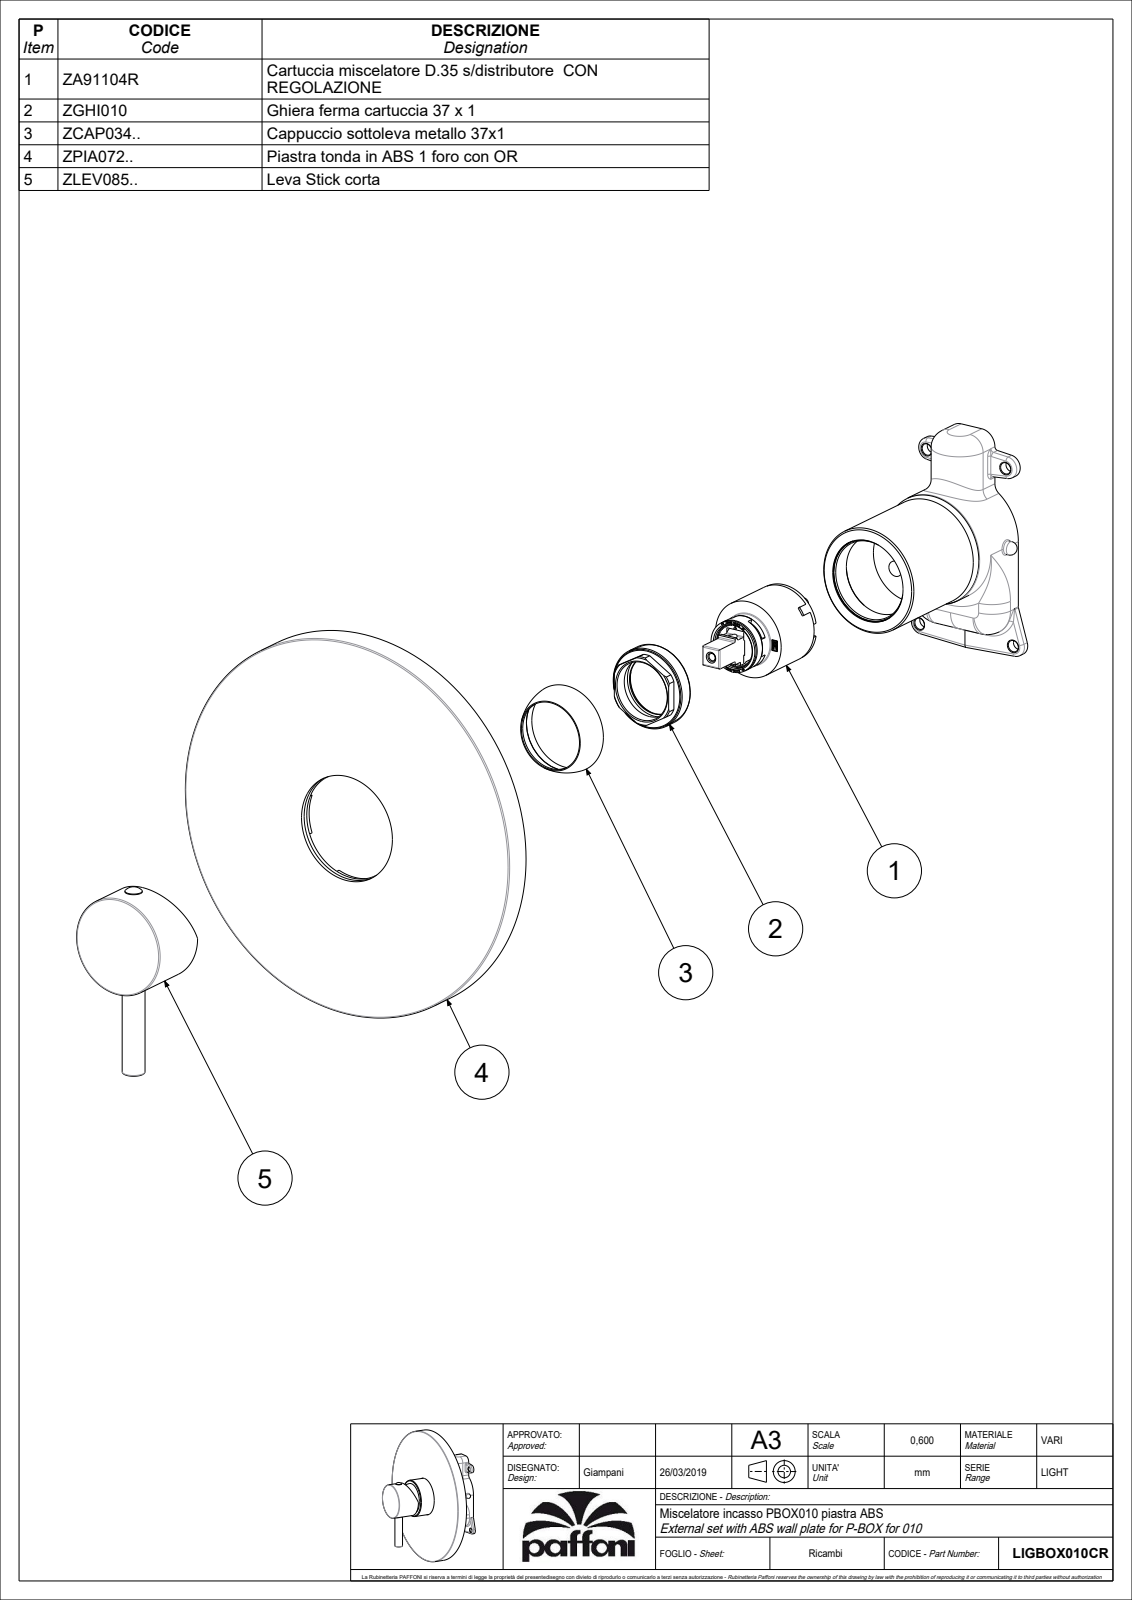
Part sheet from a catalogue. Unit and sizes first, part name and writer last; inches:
Units: inches
Overall size (bounding box): 6.811 × 6.811 × 2.567
Round holes (diameter × count): ⌀0.118 ×1
Round bosses / shafts (diameter × count): ⌀6.811 ×1, ⌀1.894 ×1, ⌀1.752 ×1, ⌀0.394 ×1, ⌀0.299 ×1, ⌀0.217 ×1, ⌀0.197 ×1
Partial cylindrical surfaces — rounded edges, fillets, slot ends (radius × count): R0.02 ×8
Main face-to-face distances: 0.512, 1.299, 2.394, 1.882, 1.811, 0.583, 0.787, 1.094, 2.354, 1.843
Volume: 22.77 in³ · Surface area: 107.2 in²
Bodies: 1 solid, 154 faces (29 planar, 44 cylindrical, 81 other)
Part name (STEP PRODUCT): LIGBOX010CR
STEP written by: CREO PARAMETRIC BY PTC INC, 2020044 (CONFIG_CONTROL_DESIGN)
